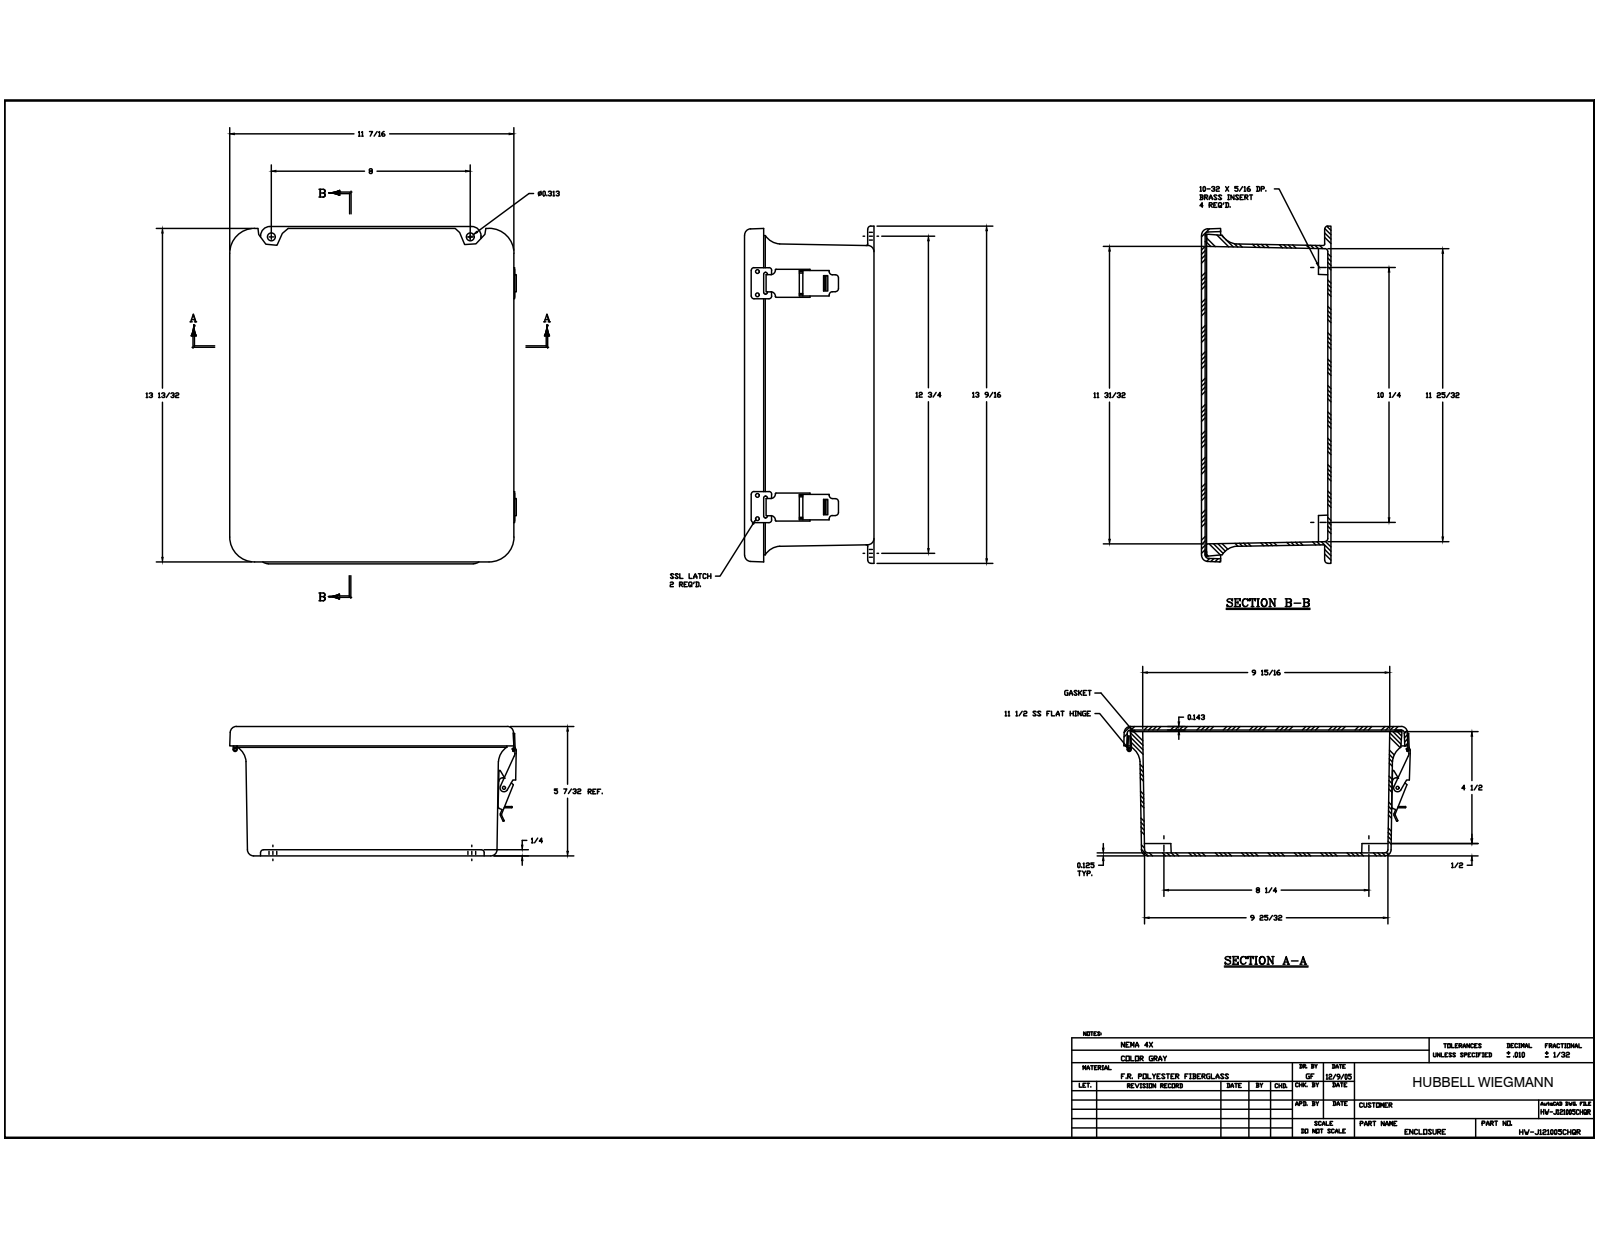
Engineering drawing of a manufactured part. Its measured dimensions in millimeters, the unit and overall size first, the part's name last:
Units: millimetres
Overall size (bounding box): 344.49 × 293.3 × 132.92
Round holes (diameter × count): ⌀3.56 ×20, ⌀2.64 ×8, ⌀3.33 ×8, ⌀3.86 ×5, ⌀3.3 ×4, ⌀3.96 ×4, ⌀5.54 ×4, ⌀3.43 ×2, ⌀9.52 ×2, ⌀2.16 ×1, ⌀2.16 ×1
Round bosses / shafts (diameter × count): ⌀3.17 ×16, ⌀6.35 ×8, ⌀6.86 ×4, ⌀7.62 ×1, ⌀4.31 ×1, ⌀3.94 ×1, ⌀3.05 ×1
Partial cylindrical surfaces — rounded edges, fillets, slot ends (radius × count): R3.17 ×22, R0.38 ×20, R0.79 ×20, R1.14 ×16, R0.76 ×12, R0.57 ×9, R6.35 ×8, R1.52 ×6
Main face-to-face distances: 3.63, 129.29, 132.92, 3.18, 126.11, 129.74, 3.17, 123.82, 127, 2.29
Hole centre spacings: 228.6, 23.81, 19.05, 229.39, 37.26, 55.65, 92.07, 92.08
Volume: 1 430 000 mm³ · Surface area: 772 921 mm²
Bodies: 38 solids, 979 faces (423 planar, 409 cylindrical, 147 other)
Part name (STEP PRODUCT): J1210HL_1; RMINS45821P_101; RMINS45821P_102; RMINS45821P_103 (+8 more)
STEP written by: Autodesk Inventor 2014 (AUTOMOTIVE_DESIGN)
